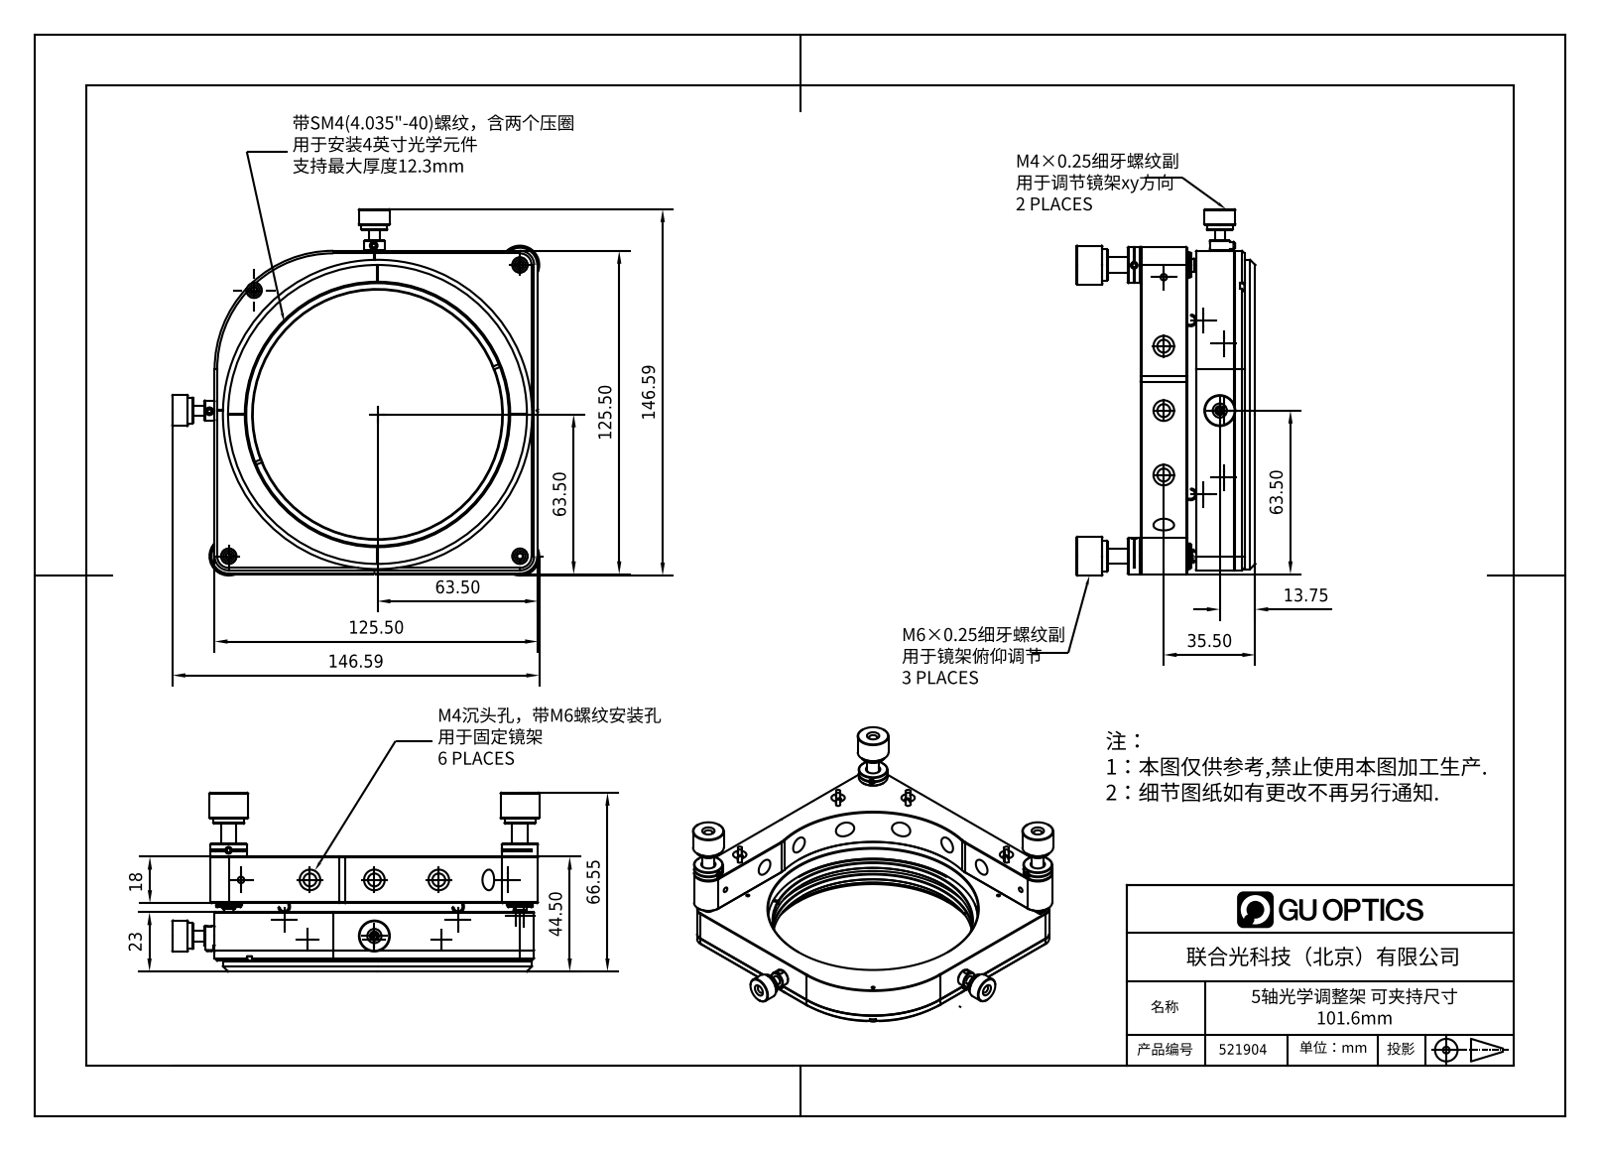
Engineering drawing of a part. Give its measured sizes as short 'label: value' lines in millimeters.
name: 521904五维光学调整镜架
written by: SolidWorks 2020 (CONFIG_CONTROL_DESIGN)
unit: mm
bodies: 71 solids, 1829 faces (628 planar, 610 cylindrical, 591 other)
size: 142.38 × 142.11 × 69.33
volume: 188 742 mm³; area: 113 015 mm²
holes: 20× ⌀2.5, 8× ⌀1.5, 7× ⌀6.5, 6× ⌀5, 6× ⌀6.2, 6× ⌀8, 4× ⌀2.4, 4× ⌀3.4, 4× ⌀6, 3× ⌀1.8, 3× ⌀3.99, 3× ⌀4
bosses: 16× ⌀3, 6× ⌀4, 6× ⌀2, 5× ⌀12, 5× ⌀5, 3× ⌀15, 3× ⌀14, 3× ⌀9.5
rounds: 36× R0.2, 18× R1.5, 12× R0.75, 12× R1, 12× R3, 10× R10, 8× R1.05, 7× R5
face distances: 8.5, 6.5, 15, 4, 10, 3.9, 18.9, 12.4, 3.5, 12.5
hole spacings: 67.5, 5.5, 23.27, 25, 26, 26.04, 33.14, 34.14
